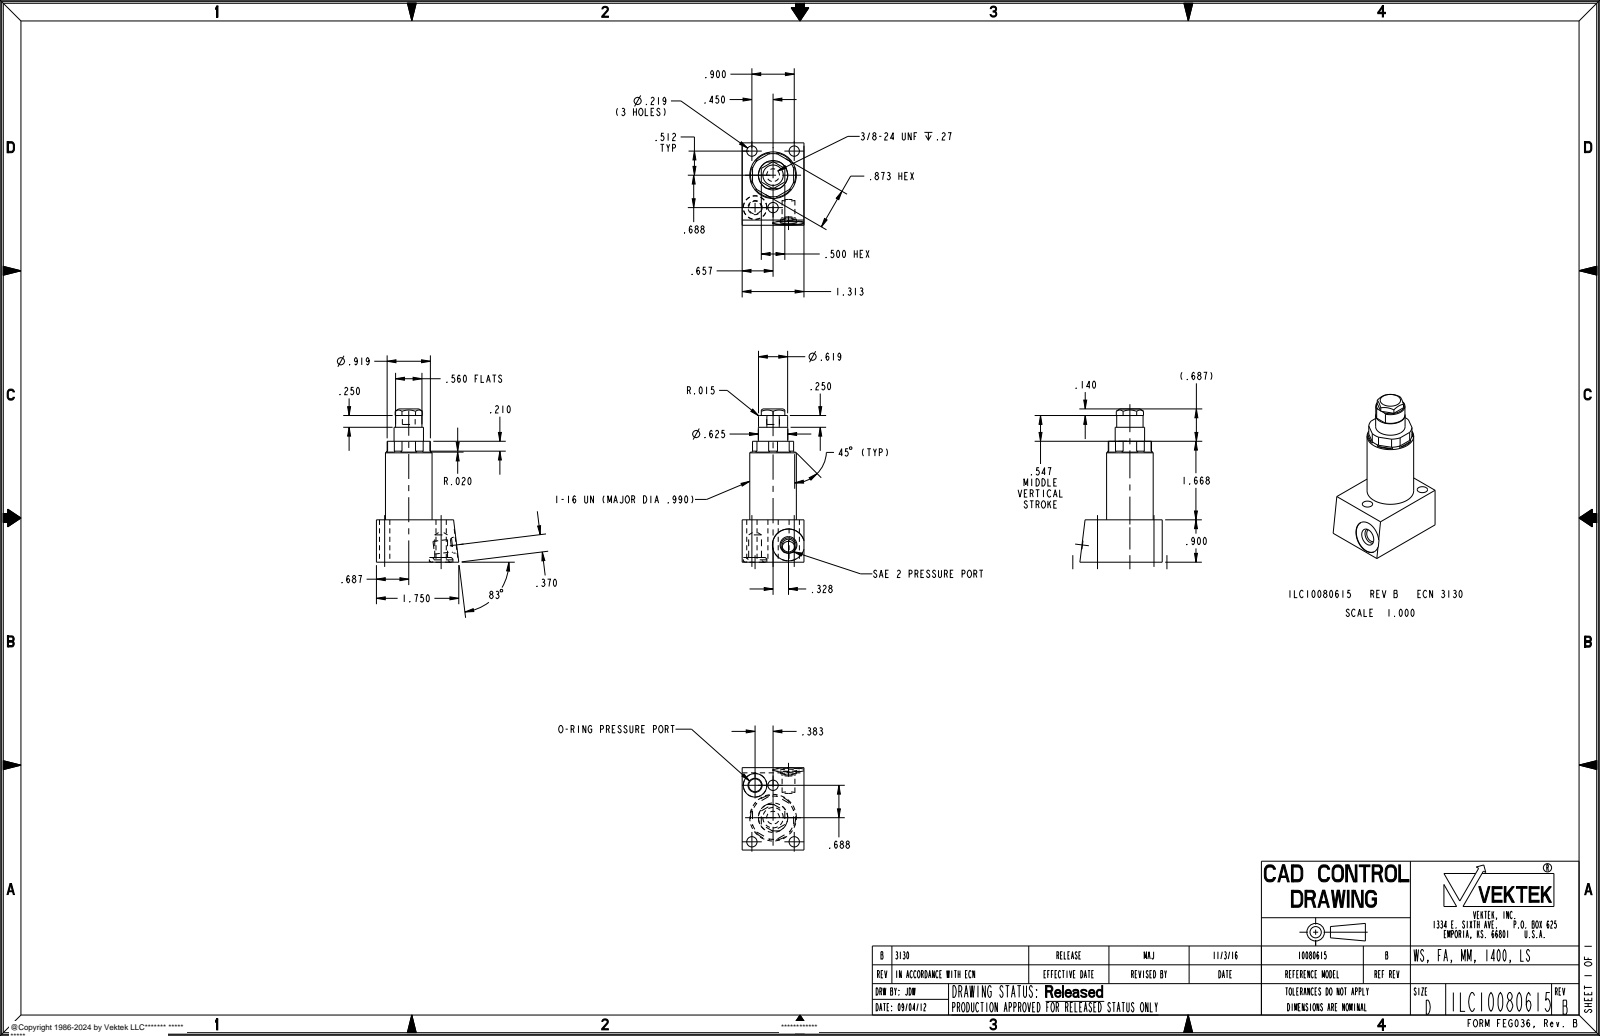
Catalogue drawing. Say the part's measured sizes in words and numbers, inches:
The part is named "ILC10080615". Its 3-D file was written by "PRO/ENGINEER BY PARAMETRIC TECHNOLOGY CORPORATION, 2007460 (AUTOMOTIVE_DESIGN_CC2)". It is 1 solid with 91 faces: 39 planar, 34 cylindrical and 18 other. Overall it measures 3.255 by 1.75 by 1.313 inches. Its volume is 3.262 cubic inches and its surface area 19.5 square inches. Round holes: 3 of diameter 0.219, 3 of diameter 0.272, 1 of diameter 0.5, 1 of diameter 0.682. Round bosses or shafts: 1 of diameter 0.99, 1 of diameter 0.625. Partial cylindrical surfaces (rounded edges, fillets, slot ends): 6 of radius 0.02, 1 of radius 0.309, 1 of radius 0.459. The main face-to-face distances are 1.313, 0.9, 2.568, 1.668, 0.187, 0.687, 0.873, 3.255, 2.355, 0.687. The hole center spacings are 0.681, 1.281, 0.383, 0.688, 0.787, 0.9, 1.202, 1.461.
